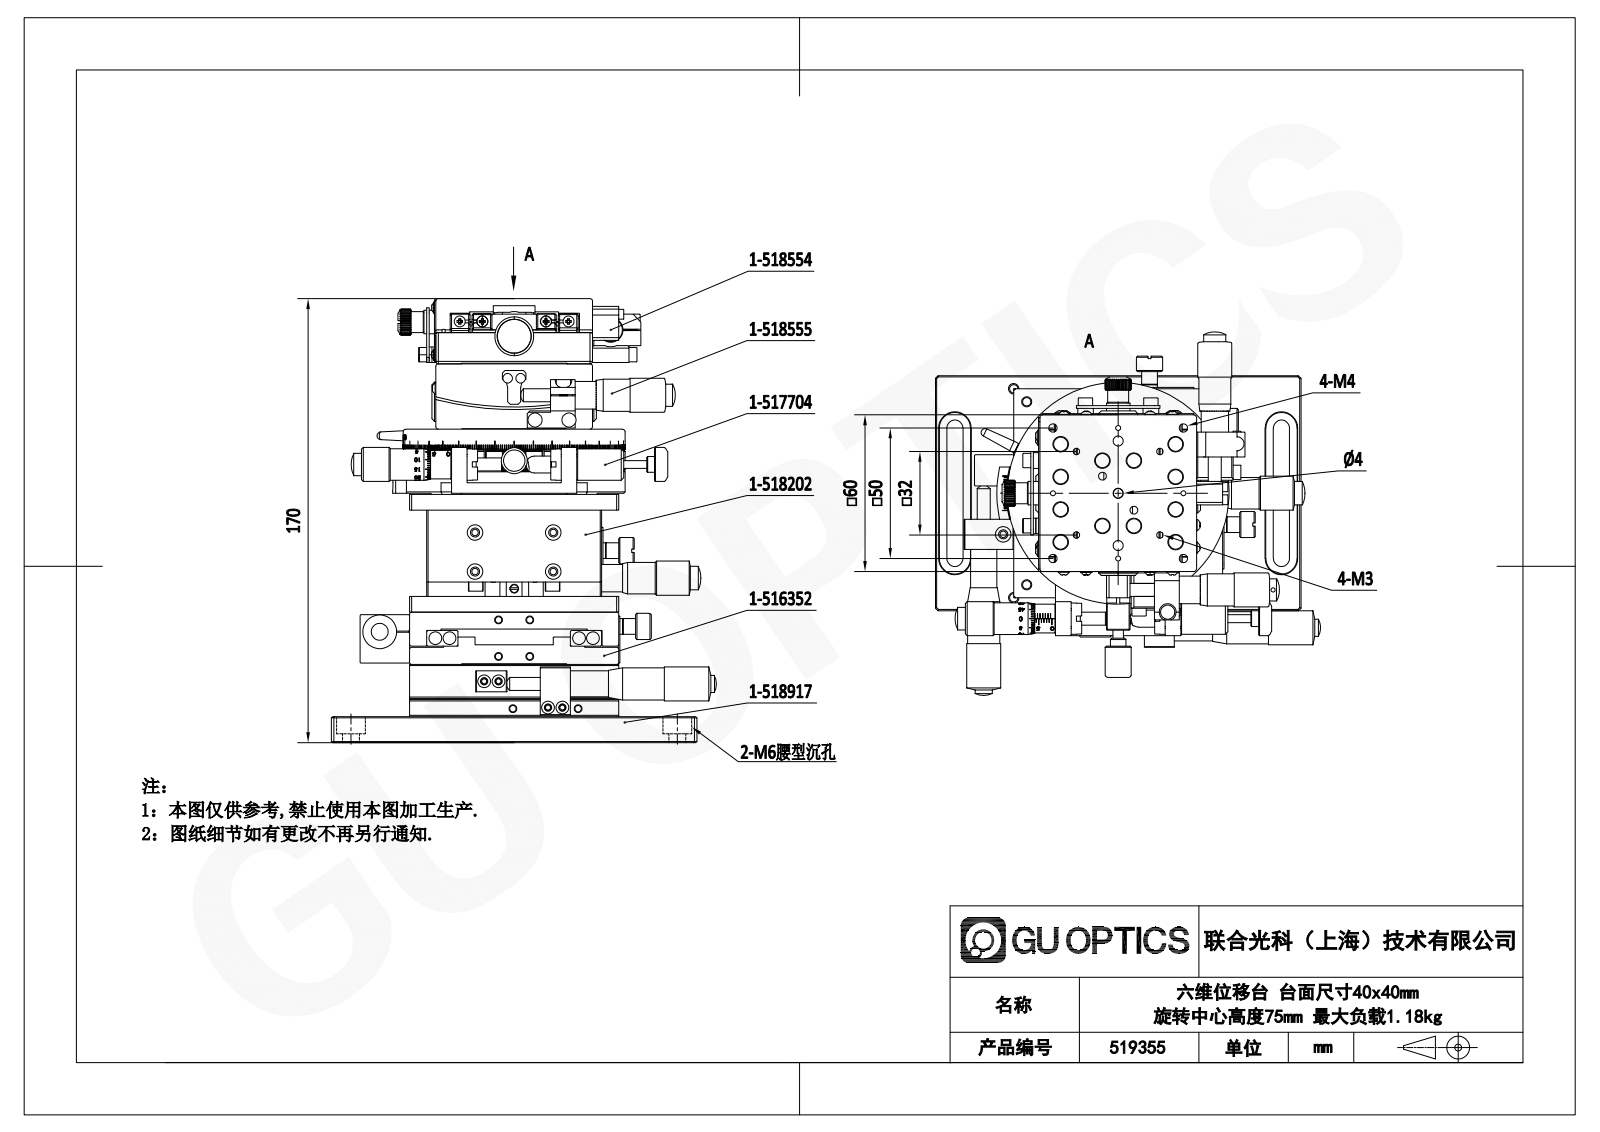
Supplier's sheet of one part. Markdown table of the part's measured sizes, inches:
| quantity | value |
| --- | --- |
| part name | 518917; 516352; 518554; 517704 (+3 more) |
| STEP written by | SolidWorks 2020 (CONFIG_CONTROL_DESIGN) |
| units | inches |
| bodies | 28 solids, 6635 faces (4074 planar, 1305 cylindrical, 1256 other) |
| overall size | 6.693 × 5.806 × 5.48 |
| volume | 44.48 in³ |
| surface area | 481.4 in² |
| round holes (diameter × count) | 0.236 × 54, 0.097 × 50, 0.173 × 28, 0.097 × 26, 0.13 × 25, 0.062 × 24, 0.126 × 24, 0.098 × 20, 0.128 × 17, 0.197 × 16, 0.079 × 14, 0.138 × 14 |
| round bosses / shafts (diameter × count) | 0.024 × 190, 0.217 × 21, 0.197 × 14, 0.118 × 12, 0.236 × 10, 0.171 × 8, 0.165 × 8, 0.394 × 7 |
| partial cylindrical surfaces (radius × count) | 0.039 × 43, 0.079 × 32, 0.059 × 8, 0.067 × 4, 0.086 × 4, 0.089 × 4, 0.122 × 4, 0.138 × 4 |
| main face-to-face distances | 0.787, 0.256, 1.969, 0.394, 0.531, 0.02, 1.535, 1.575, 0.984, 3.74 |
| hole center spacings | 0.984, 1.433, 1.181, 0.591, 1.772, 2.395, 2.735, 2.201 |
